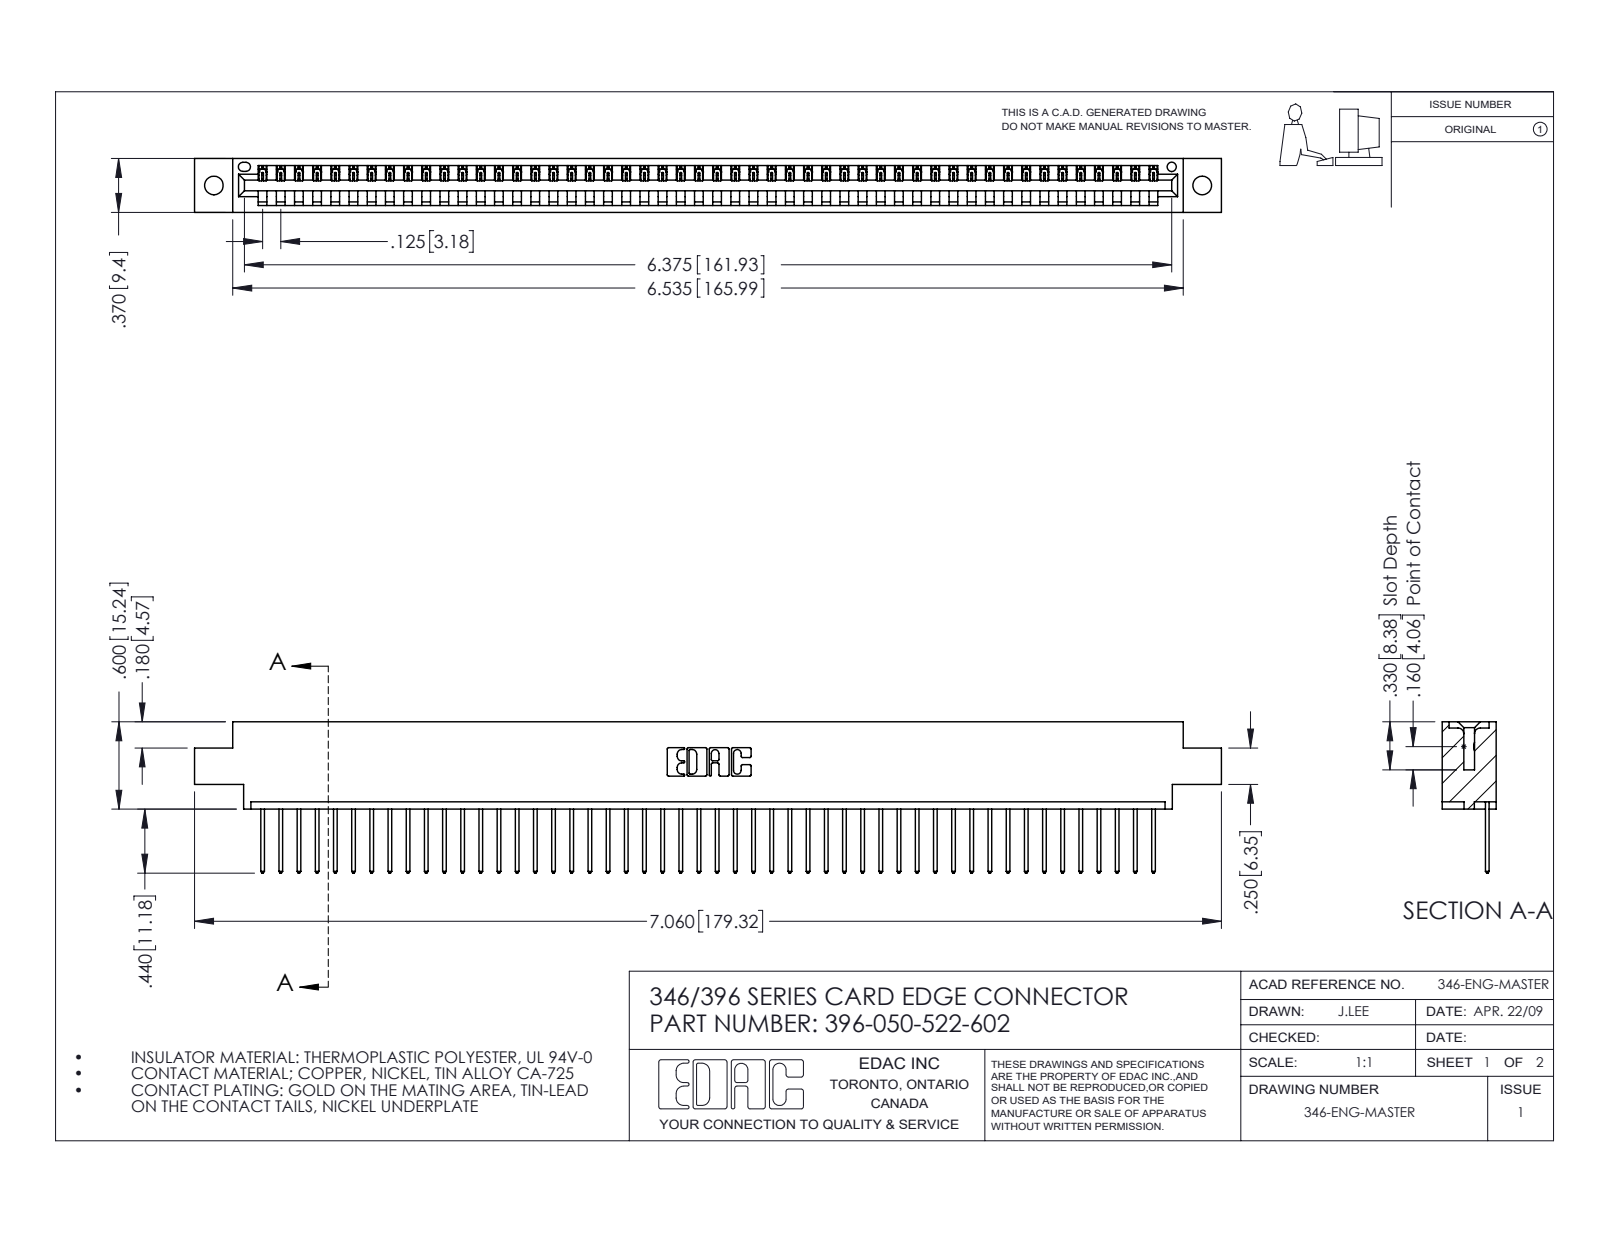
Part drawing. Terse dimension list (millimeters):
name: 396-050-522-602; 345-292-001_345-293-122; 346 Part_0.170 Offset - 0.128 Dia
written by: SolidWorks 2016 (CONFIG_CONTROL_DESIGN)
unit: mm
bodies: 51 solids, 3026 faces (2080 planar, 946 cylindrical, 0 other)
size: 179.3 × 26.4 × 9.4
volume: 17 040 mm³; area: 21 450 mm²
holes: 2× ⌀3.3, 1× ⌀1.6
rounds: 100× R0.2, 100× R0.3, 22× R0.3, 6× R0.2, 6× R0.8, 3× R0.7, 2× R0.8, 2× R1
face distances: 1.2, 8.2, 9.4, 6.4, 1.8, 7.6, 0.6, 3.8, 5.6, 2.5
hole spacings: 6.2, 167.3, 172.6
